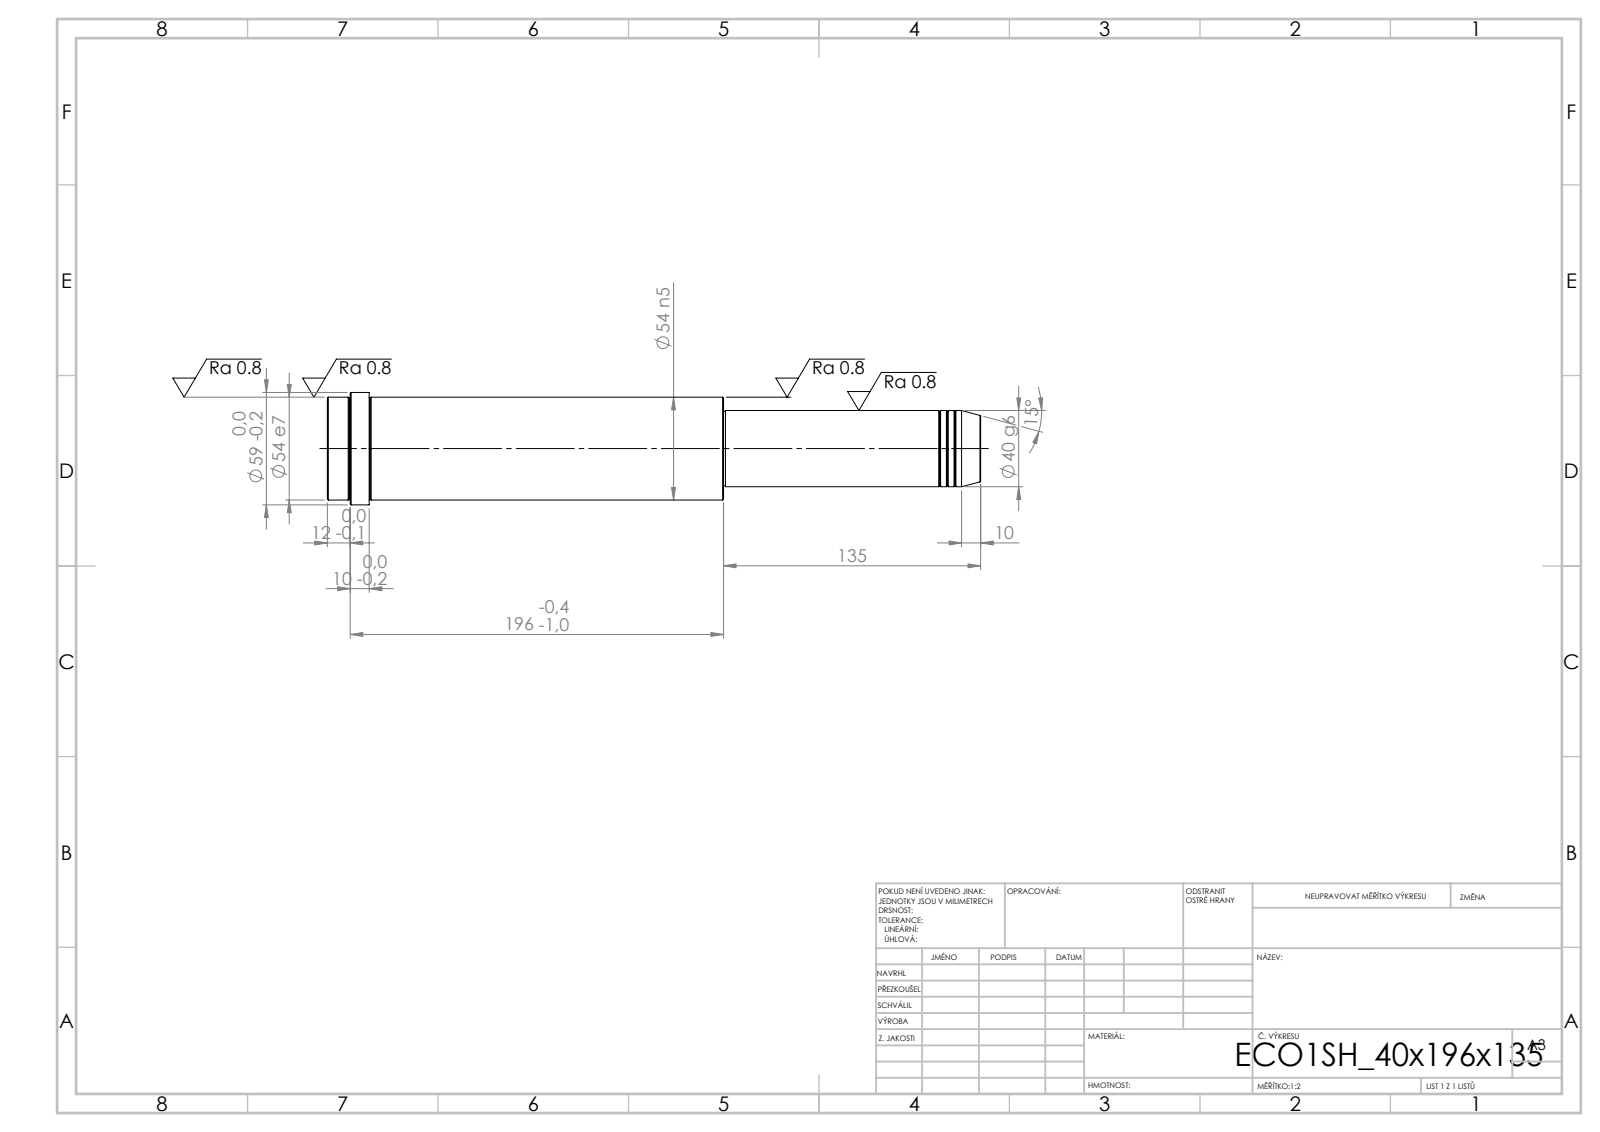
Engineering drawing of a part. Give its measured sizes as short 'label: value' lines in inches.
written by: SolidWorks 2019 (CONFIG_CONTROL_DESIGN)
unit: in
bodies: 1 solid, 52 faces (6 planar, 16 cylindrical, 30 other)
size: 13.504 × 2.323 × 2.323
volume: 39.57 in³; area: 89.69 in²
bosses: 1× ⌀2.323, 1× ⌀2.126, 1× ⌀1.575, 1× ⌀1.535
face distances: 8.189, 5.315, 13.504, 12.638, 7.323, 0.866, 13.031, 7.717, 0.394, 0.472
